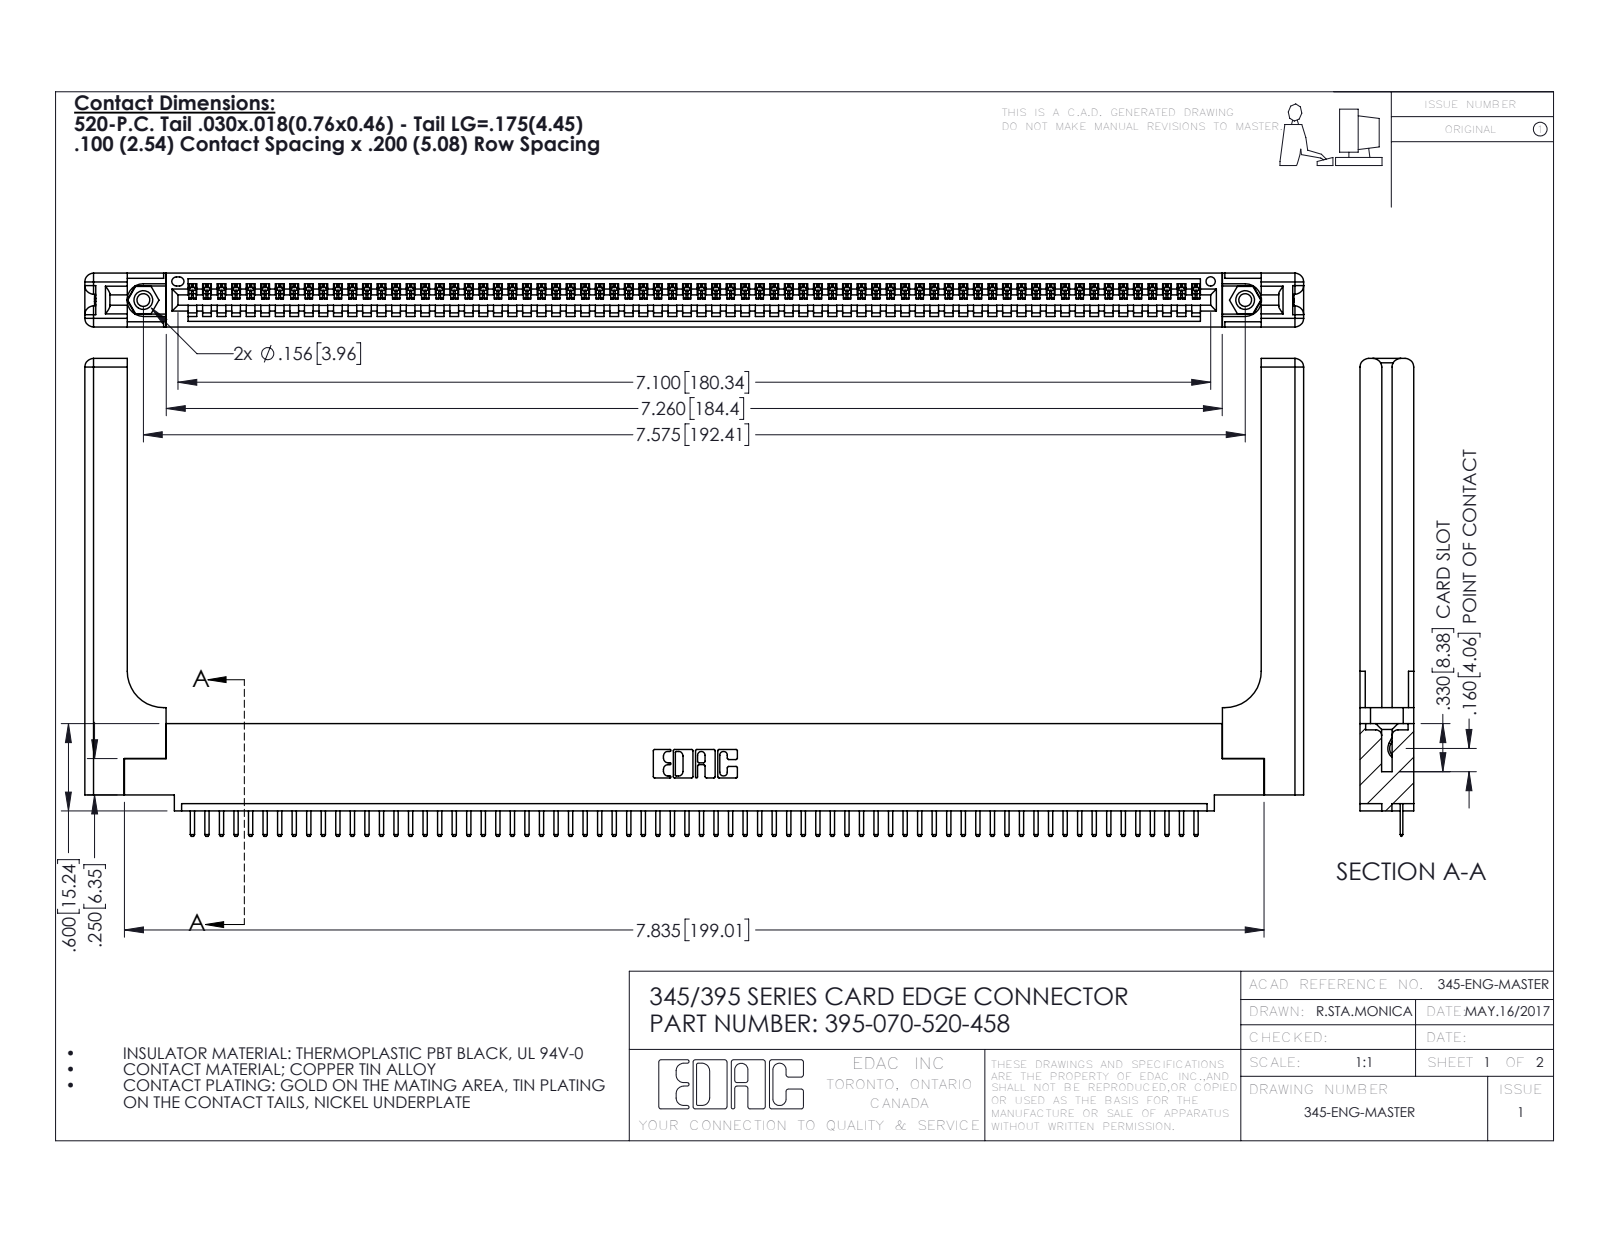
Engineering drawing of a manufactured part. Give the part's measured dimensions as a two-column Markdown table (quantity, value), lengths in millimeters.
| quantity | value |
| --- | --- |
| part name | 395-070-520-458; 345-250-001_345-250-001-102; 345-220-058_345-220-058; 345 Part_0.110 Offset - 0.156 Dia-TH (+1 more) |
| STEP written by | SolidWorks 2016 (CONFIG_CONTROL_DESIGN) |
| units | millimeters |
| bodies | 75 solids, 4726 faces (3172 planar, 1494 cylindrical, 60 other) |
| overall size | 212.8 × 83.4 × 9.4 |
| volume | 28 680 mm³ |
| surface area | 31 910 mm² |
| round holes (diameter × count) | 2.3 × 2, 3.2 × 2, 4 × 2, 1.6 × 1 |
| round bosses / shafts (diameter × count) | 3.9 × 2 |
| partial cylindrical surfaces (radius × count) | 0.3 × 142, 0.2 × 140, 0.3 × 22, 1.5 × 16, 0.2 × 6, 0.8 × 6, 0.7 × 3, 0.8 × 2 |
| main face-to-face distances | 1.8, 9.4, 7.6, 2.5, 6.9, 0.6, 5.1, 5.7, 3.8, 3.8 |
| hole center spacings | 6.9, 186.4, 192.4 |
